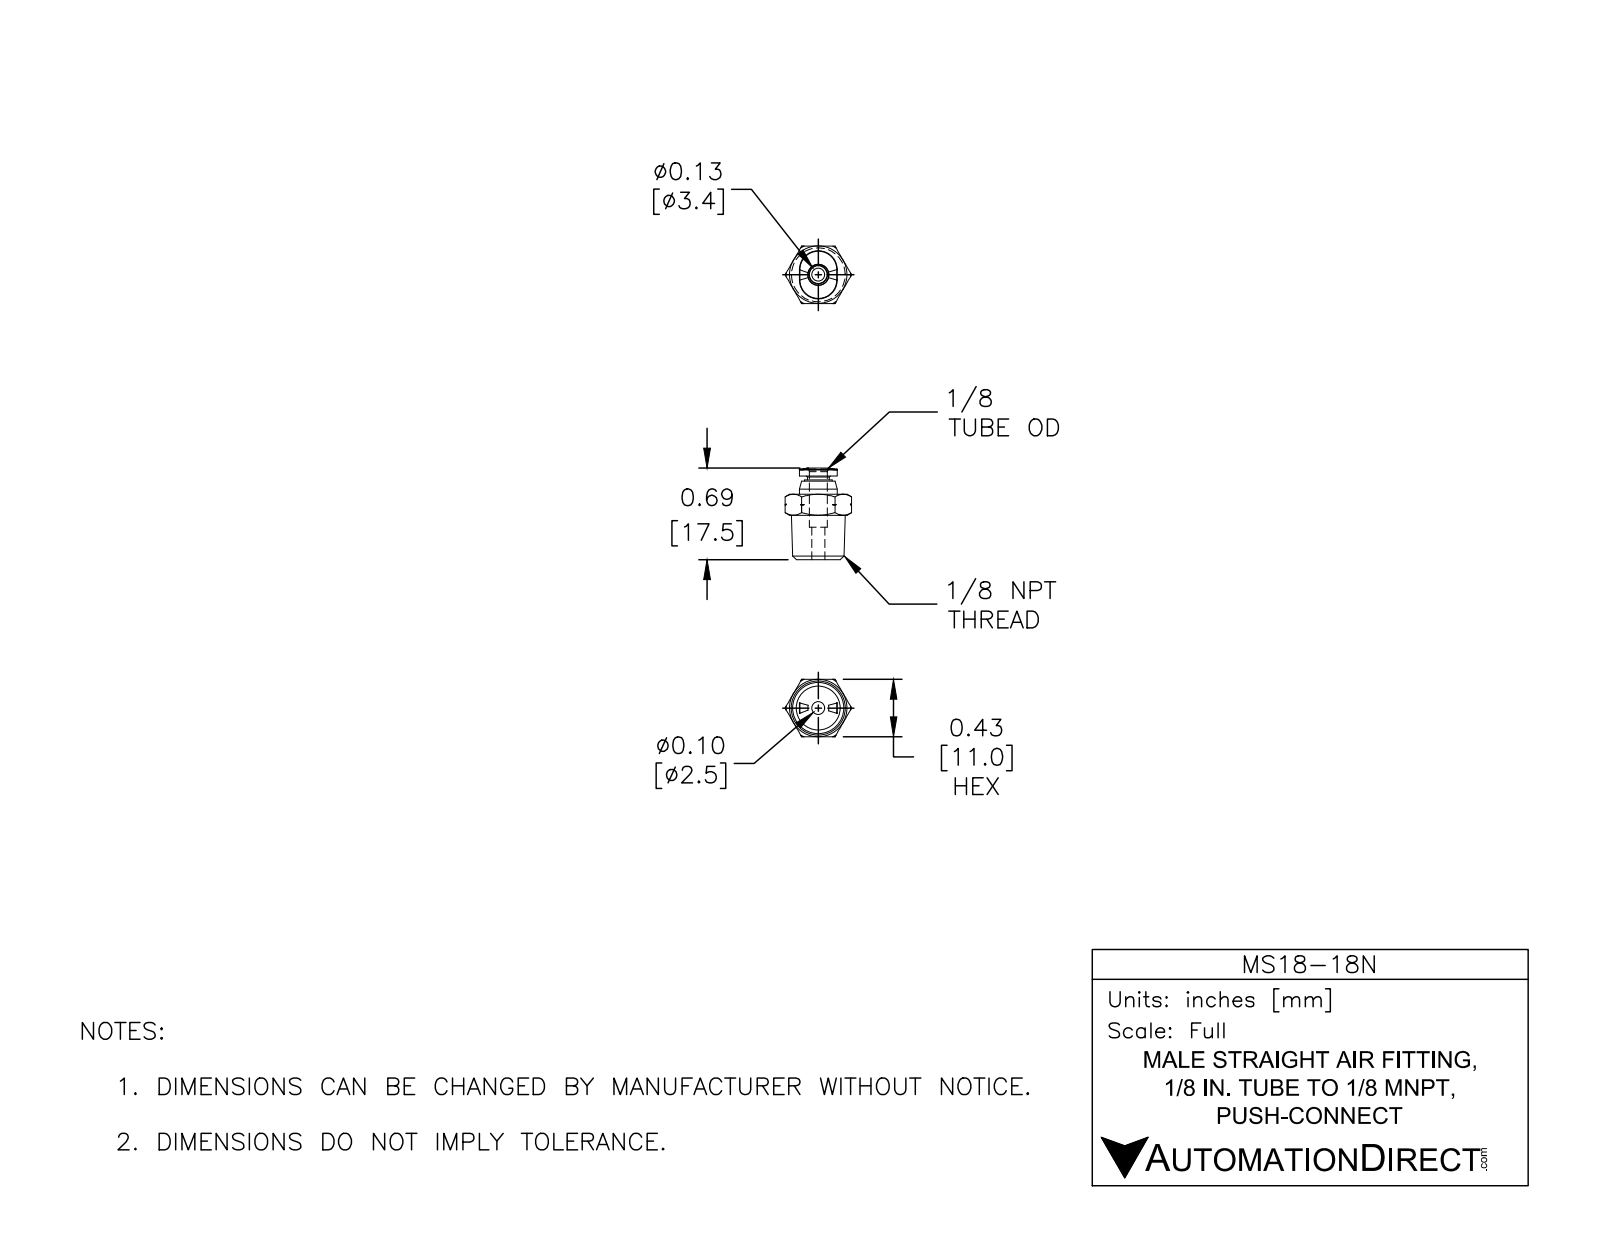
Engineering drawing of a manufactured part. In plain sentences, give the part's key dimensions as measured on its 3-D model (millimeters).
The part is named "MS18-18N". Its 3-D file was written by "SolidWorks 2015 (CONFIG_CONTROL_DESIGN)". It is 1 solid with 80 faces: 16 planar, 12 cylindrical and 52 other. Overall it measures 17.5 by 12.7 by 11 millimeters. Its volume is 1 100 cubic millimeters and its surface area 932 square millimeters. Round holes: 1 of diameter 2.5, 1 of diameter 3.4. Round bosses or shafts: 1 of diameter 7.2, 1 of diameter 5.3, 1 of diameter 4.2. Partial cylindrical surfaces (rounded edges, fillets, slot ends): 2 of radius 3.6. The main face-to-face distances are 11, 12.5, 16, 3.5, 8.5, 4, 7.5, 2.5, 15, 6.5.
